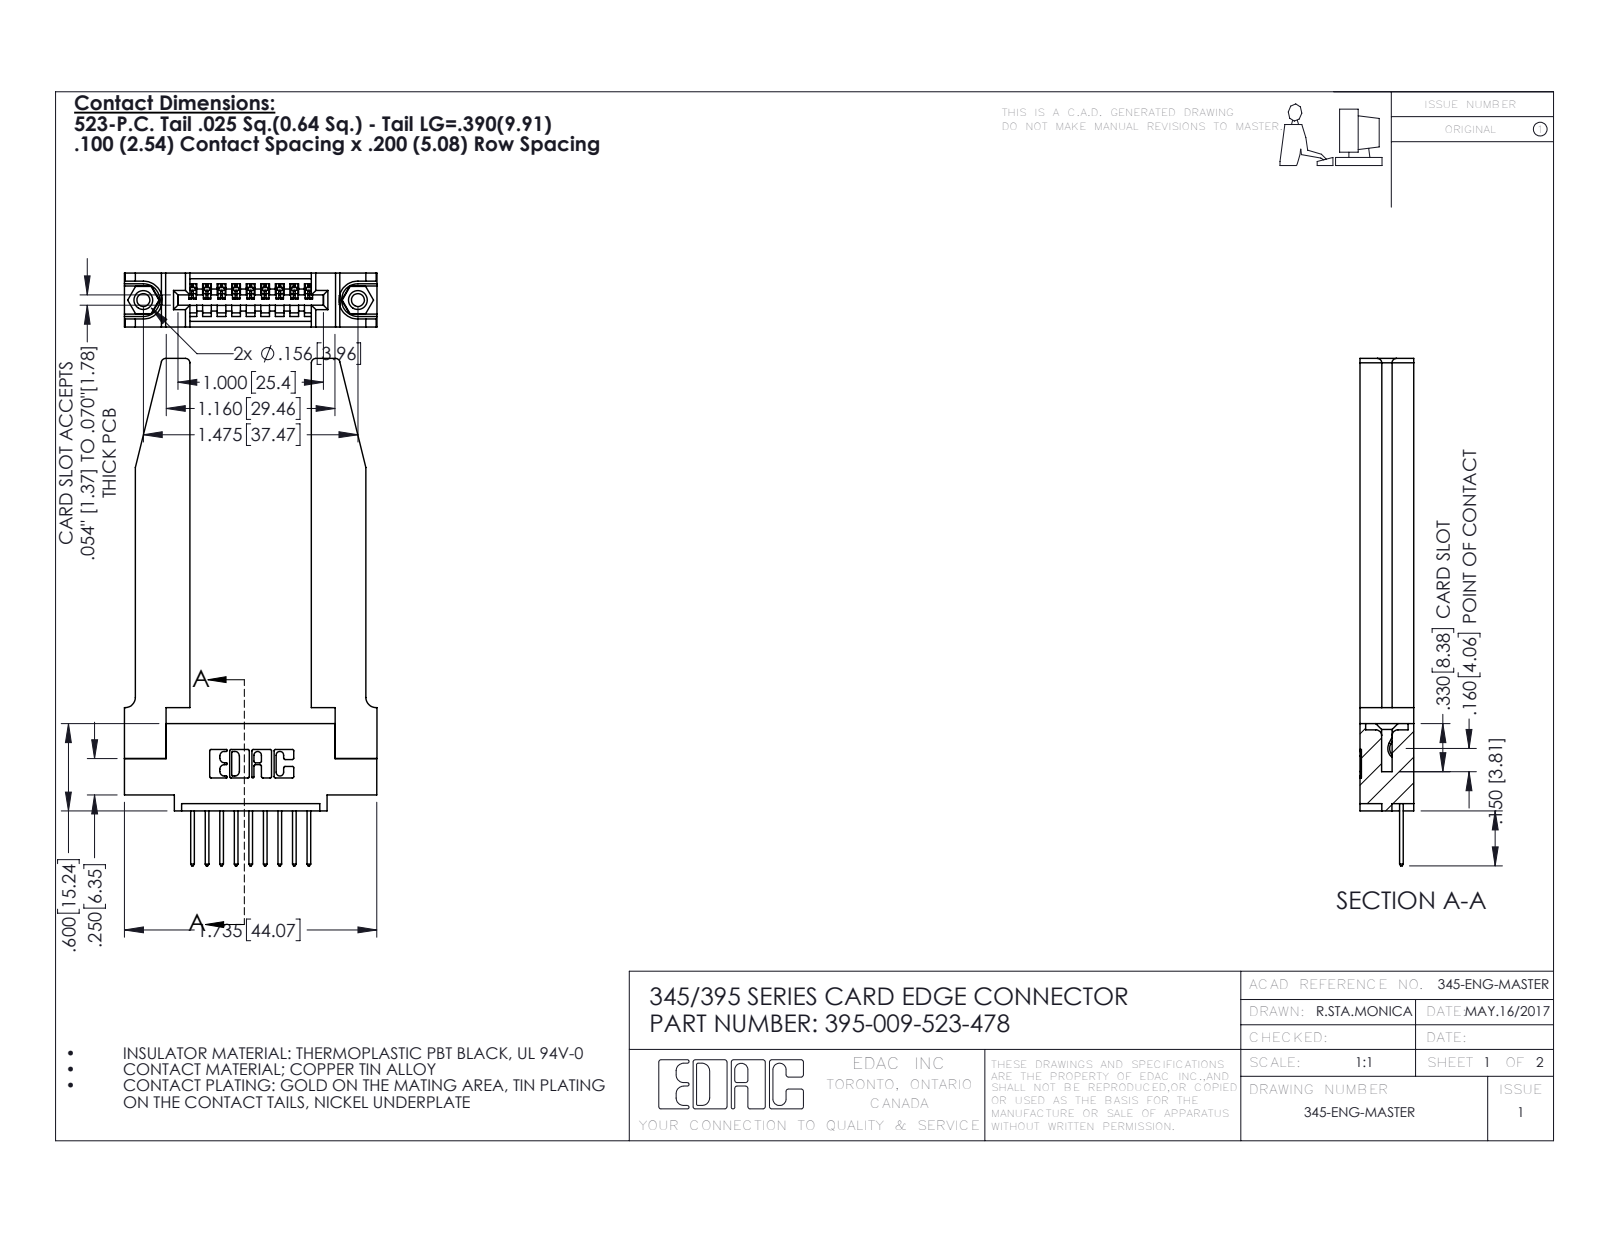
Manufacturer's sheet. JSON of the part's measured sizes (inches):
{"part_name": "345-220-078_345-220-078; 345 Part_0.110 Offset - 0.156 Dia-TH; 345-250-001_345-250-001-102; 345-292-001_345-293-123 (+1 more)", "step_written_by": "SolidWorks 2016 (CONFIG_CONTROL_DESIGN)", "units": "inches", "bodies": {"solids": 14, "faces": 886, "planar": 586, "cylindrical": 248, "other": 52}, "overall_size": [3.487, 1.736, 0.37], "volume_in3": 0.709, "surface_area_in2": 17.97, "round_holes": [[0.089, 2], [0.125, 2], [0.156, 2], [0.064, 1]], "round_bosses_or_shafts": [[0.155, 2]], "partial_cylinders_radius": [[0.01, 22], [0.006, 18], [0.01, 18], [0.03, 8], [0.007, 6], [0.031, 6], [0.026, 3], [0.031, 2]], "face_to_face_distances": [0.37, 0.072, 0.298, 0.15, 0.148, 0.22, 0.077, 0.835, 0.098, 0.272], "hole_center_spacings": [0.27, 1.244, 1.475]}
